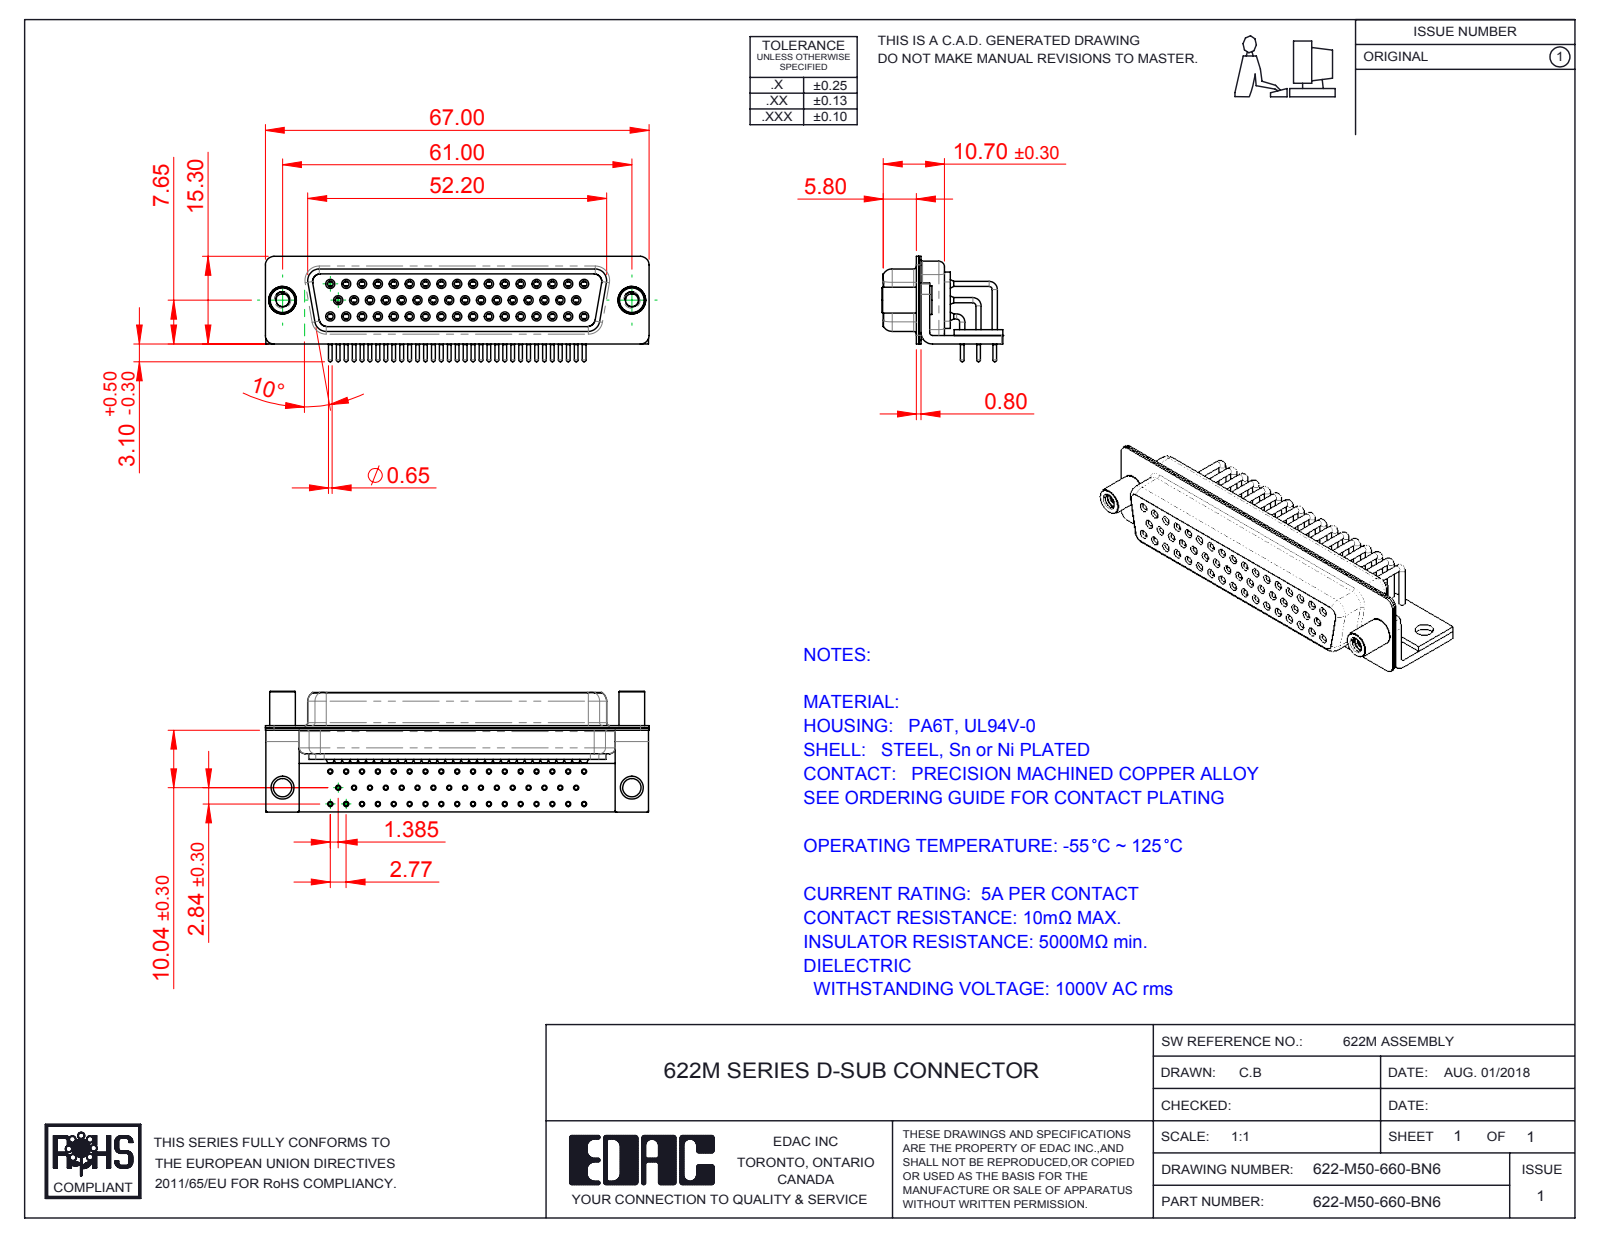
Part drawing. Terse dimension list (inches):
name: 622M Contact Row 2_50 Contacts; 622M Contact Row 1_50 Contacts; 622M Shell Rear_50 Contacts; 622M Shell Front_50 Contacts (+6 more)
written by: SolidWorks 2016 (CONFIG_CONTROL_DESIGN)
unit: in
bodies: 58 solids, 3129 faces (845 planar, 1451 cylindrical, 833 other)
size: 2.638 × 0.831 × 0.724
volume: 0.48 in³; area: 28.57 in²
holes: 50× ⌀0.035, 50× ⌀0.039, 50× ⌀0.043, 50× ⌀0.067, 50× ⌀0.071, 50× ⌀0.079, 2× ⌀0.089, 2× ⌀0.126, 2× ⌀0.157, 2× ⌀0.189
bosses: 59× ⌀0.035, 50× ⌀0.063, 50× ⌀0.059, 50× ⌀0.026, 2× ⌀0.197, 2× ⌀0.193, 2× ⌀0.177
rounds: 16× R0.01, 16× R0.059, 13× R0.079, 8× R0.053, 8× R0.063, 5× R0.02, 4× R0.024, 4× R0.026
face distances: 0.016, 0.039, 0.087, 0.033, 0.053, 0.467, 0.482, 0.228, 0.031, 0.232
hole spacings: 0.109, 0.124, 0.218, 0.327, 0.436, 0.545, 0.654, 0.763
